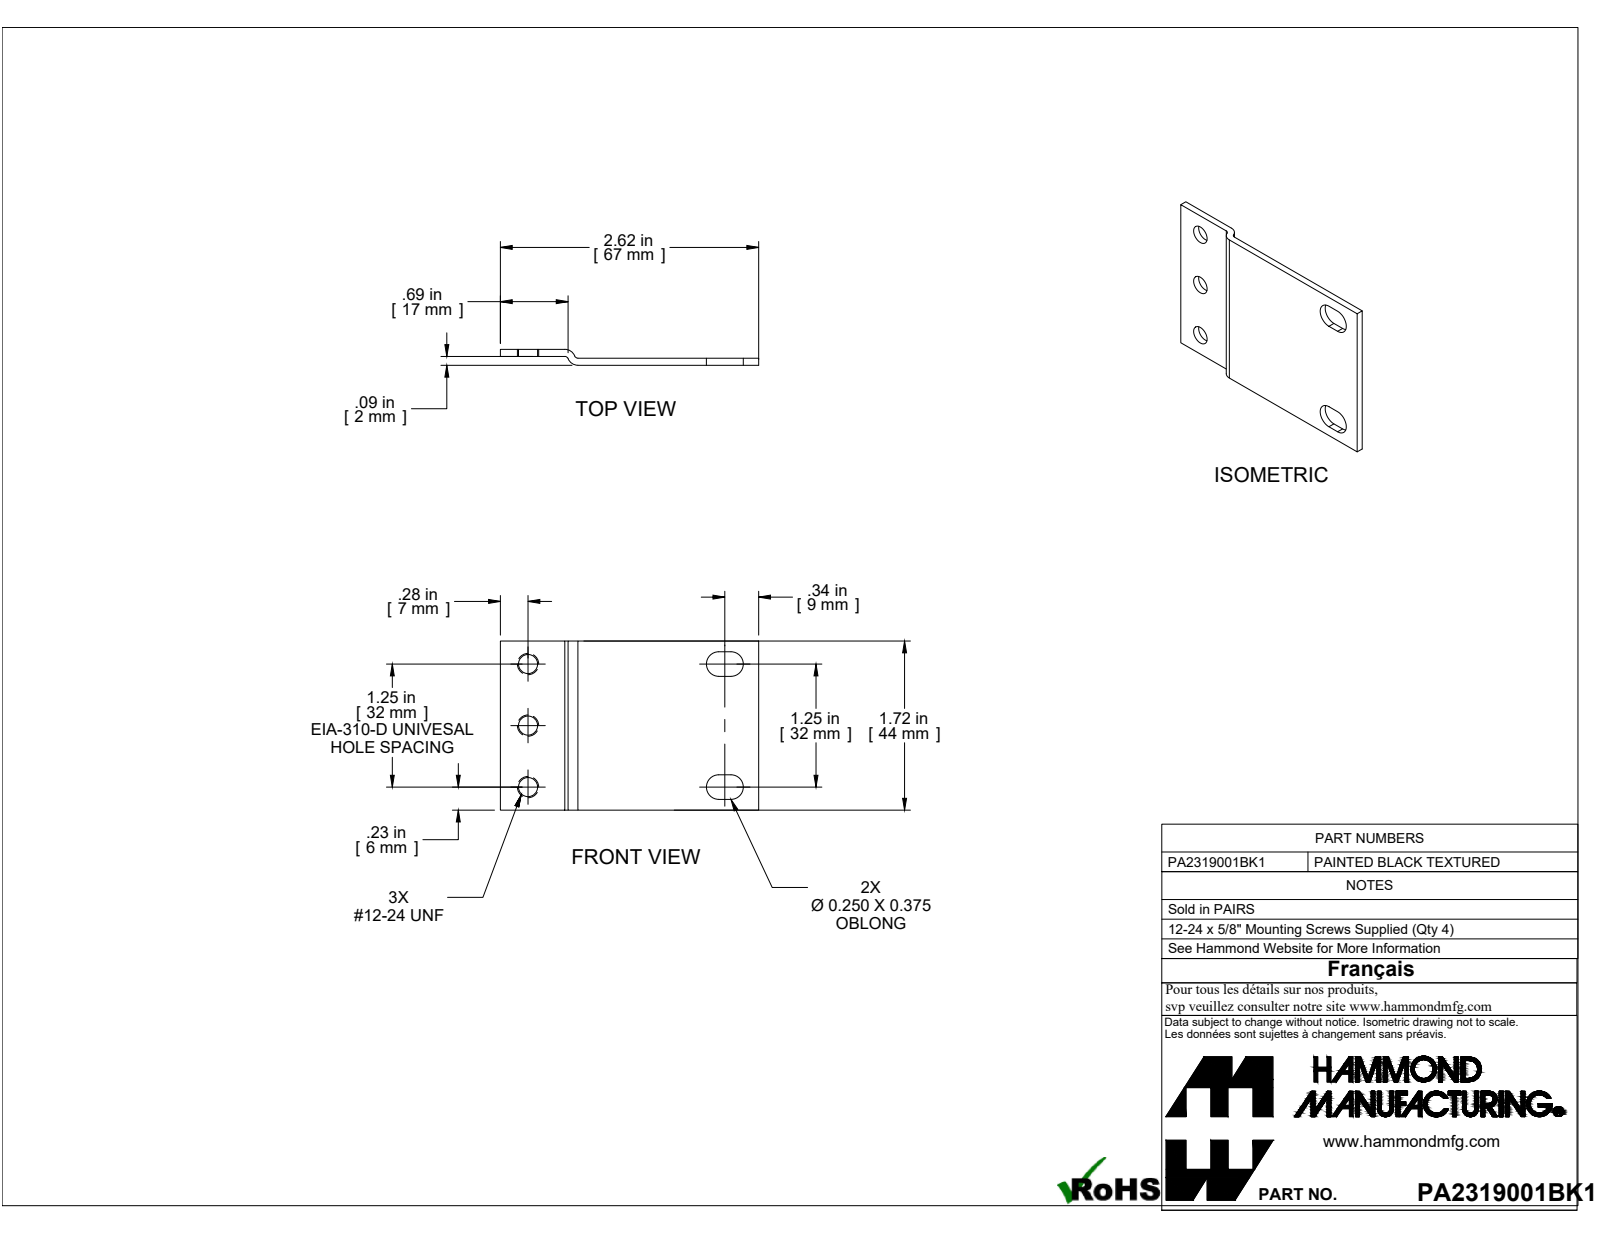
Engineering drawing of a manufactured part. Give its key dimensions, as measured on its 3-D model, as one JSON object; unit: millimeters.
{"part_name": "PA2319001BK1", "step_written_by": "SolidWorks 2019 (AUTOMOTIVE_DESIGN)", "units": "millimeters", "bodies": {"solids": 1, "faces": 23, "planar": 12, "cylindrical": 11, "other": 0}, "overall_size": [66.7, 43.6, 4.1], "volume_mm3": 5130, "surface_area_mm2": 6190, "round_holes": [[4, 3]], "partial_cylinders_radius": [[3.2, 4], [0.9, 2], [2.7, 2]], "face_to_face_distances": [1.8, 2.3, 4.1, 0.5, 2.3, 1.8, 43.6, 66.7, 2.8, 9.1], "hole_center_spacings": [15.9, 31.8]}
